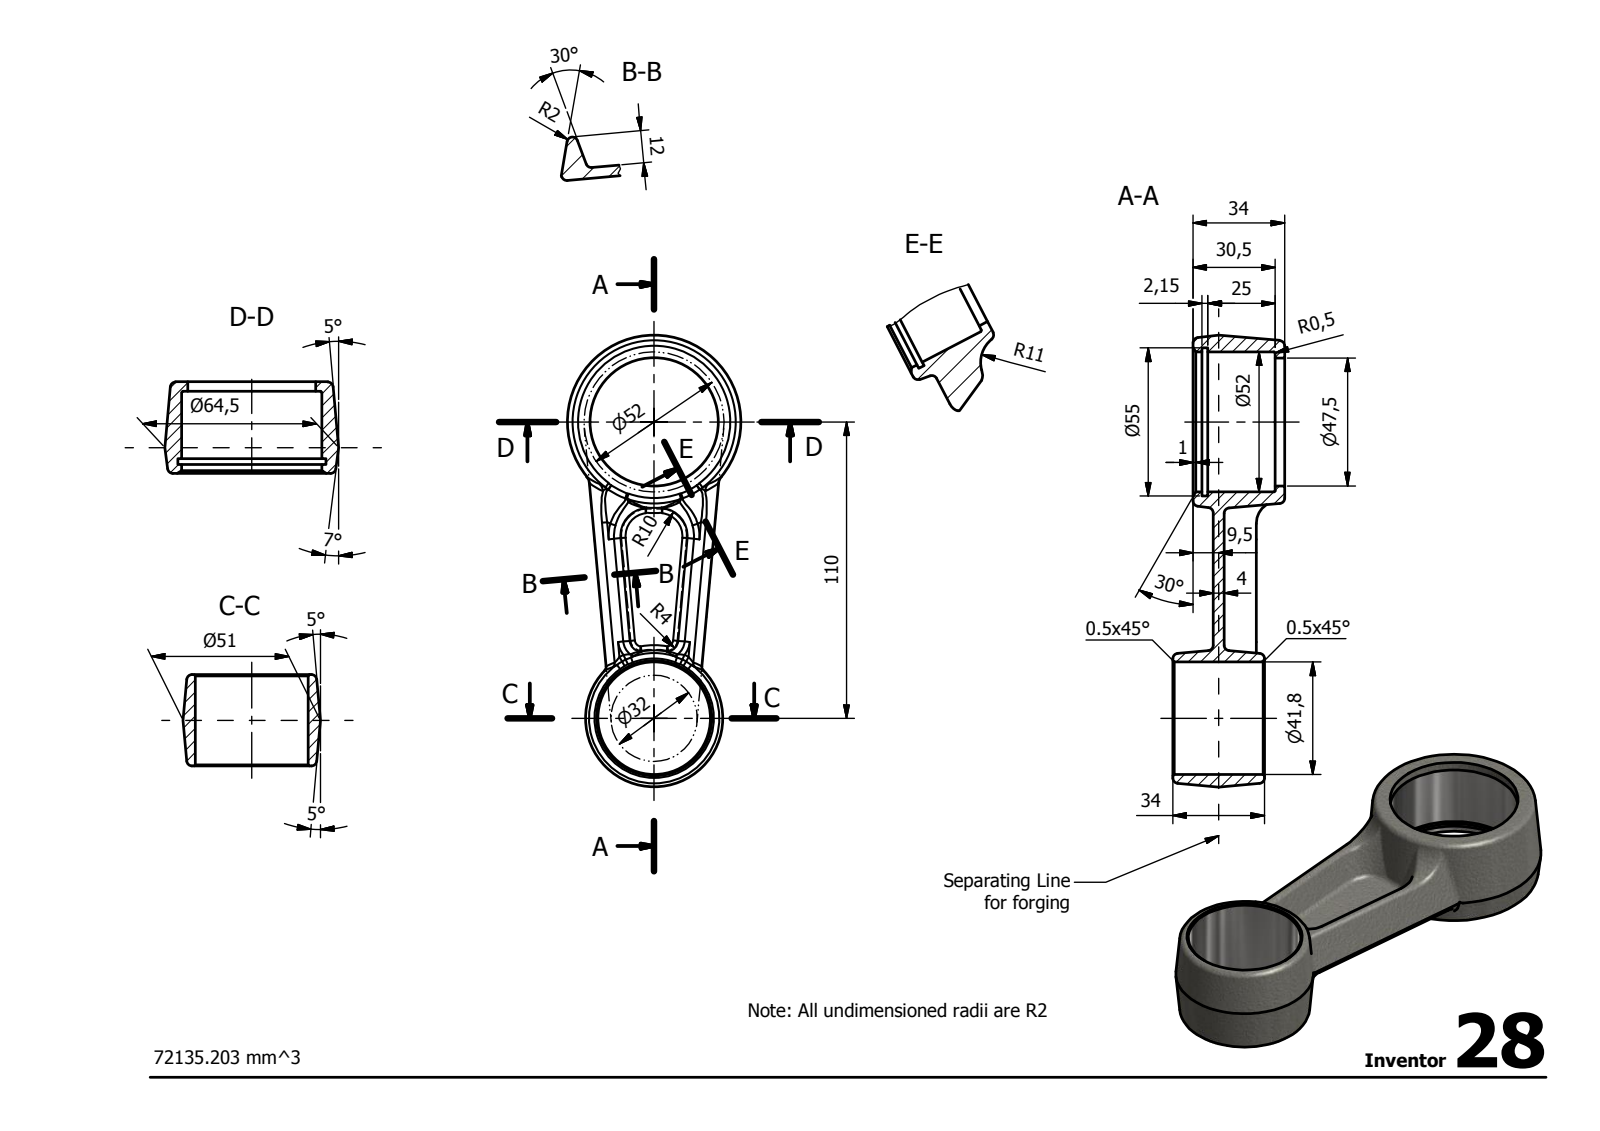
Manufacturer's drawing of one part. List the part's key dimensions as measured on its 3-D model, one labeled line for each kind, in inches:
STEP written by: Autodesk Inventor 2014 (AUTOMOTIVE_DESIGN)
Units: inches
Bodies: 1 solid, 114 faces (19 planar, 11 cylindrical, 84 other)
Overall size (bounding box): 6.604 × 2.539 × 1.634
Volume: 4.402 in³ · Surface area: 48.59 in²
Round holes (diameter × count): ⌀1.646 ×1, ⌀1.87 ×1, ⌀2.047 ×1, ⌀2.165 ×1
Partial cylindrical surfaces — rounded edges, fillets, slot ends (radius × count): R0.079 ×6
Main face-to-face distances: 0.157, 1.043, 0.886, 0.295, 0.748, 1.339, 0.453, 1.201, 0.906, 0.138
Hole centre spacings: 4.331
